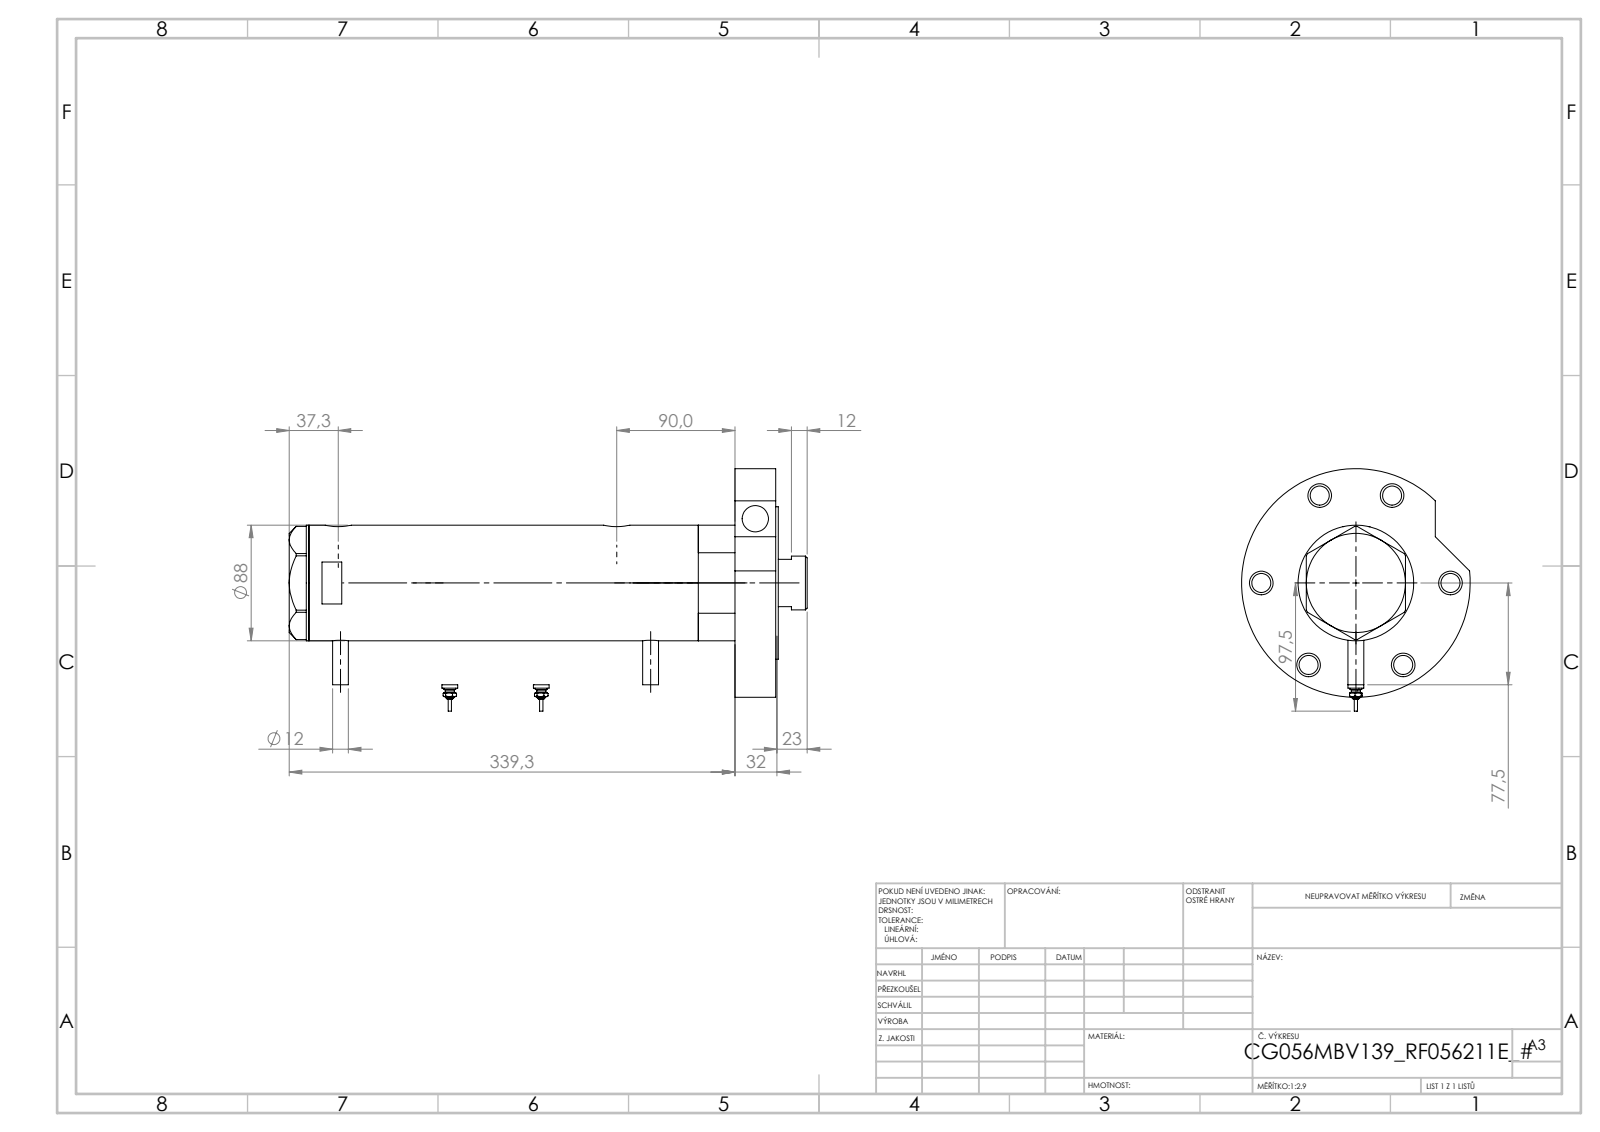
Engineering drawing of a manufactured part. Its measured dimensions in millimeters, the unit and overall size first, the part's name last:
Units: millimetres
Overall size (bounding box): 394.3 × 184.5 × 174
Round holes (diameter × count): ⌀14.5 ×7, ⌀18 ×6, ⌀20 ×3, ⌀12.5 ×2, ⌀13.16 ×2, ⌀42 ×1, ⌀43.5 ×1, ⌀56 ×1, ⌀60 ×1, ⌀75 ×1, ⌀80 ×1
Round bosses / shafts (diameter × count): ⌀12 ×4, ⌀9 ×2, ⌀7 ×2, ⌀4.5 ×2, ⌀2.5 ×2, ⌀174 ×1, ⌀116 ×1, ⌀88 ×1
Main face-to-face distances: 31, 2, 357.3, 324.3, 355.3, 33, 234.4, 89.9, 120.9, 122.9
Hole centre spacings: 72, 80, 119.73, 124.71, 129.15, 143.69, 1.7, 25.8
Volume: 2 573 000 mm³ · Surface area: 361 175 mm²
Bodies: 7 solids, 257 faces (91 planar, 102 cylindrical, 64 other)
Part name (STEP PRODUCT): V270CG_VC; V270CG_FRONT; Switch; V270CG_MIDDLE (+2 more)
STEP written by: SolidWorks 2019 (CONFIG_CONTROL_DESIGN)
